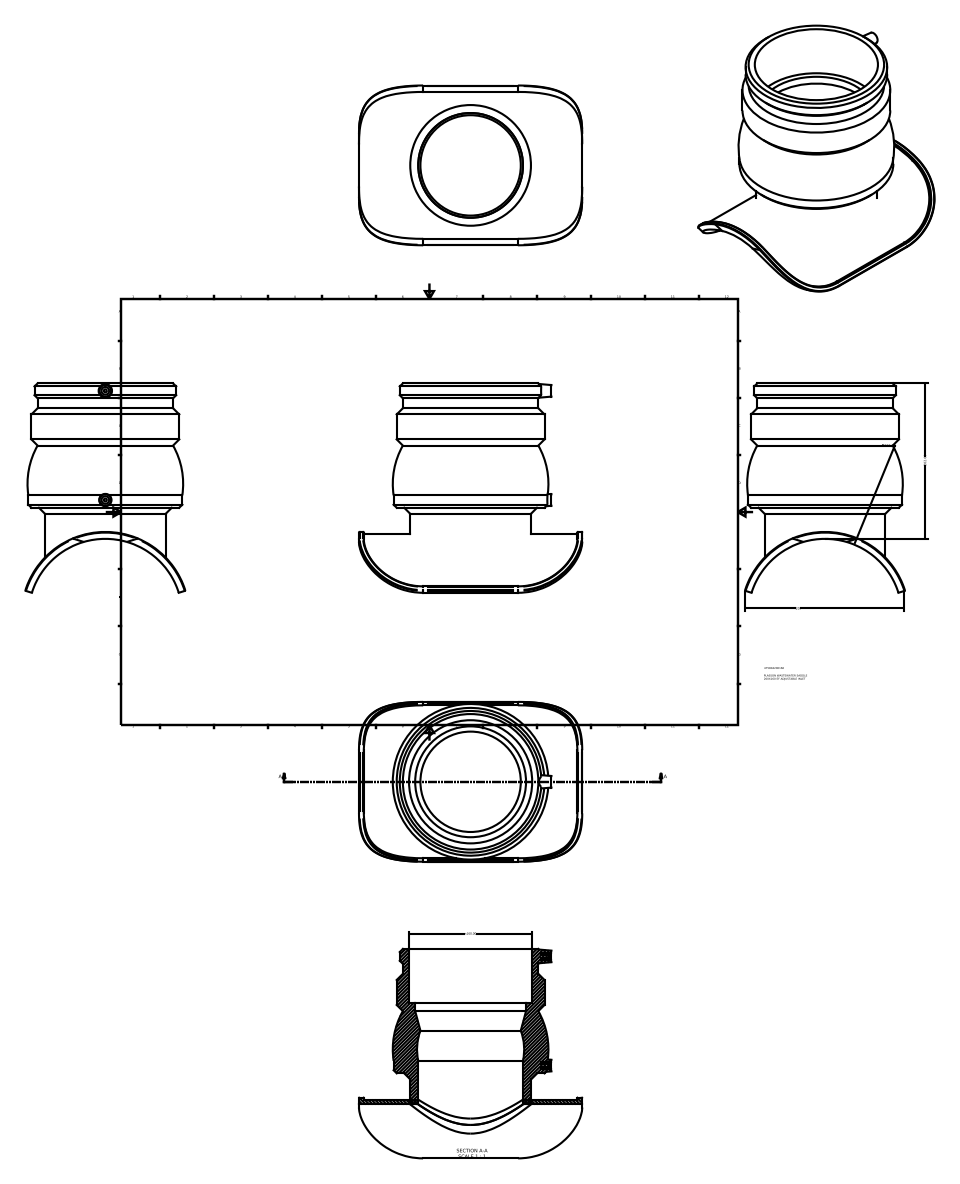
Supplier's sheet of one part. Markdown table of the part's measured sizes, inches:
| quantity | value |
| --- | --- |
| part name | 475804200160 |
| STEP written by | Autodesk Inventor 2015 (AUTOMOTIVE_DESIGN) |
| units | inches |
| bodies | 2 solids, 69 faces (17 planar, 29 cylindrical, 23 other) |
| overall size | 11.417 × 10.711 × 8.172 |
| volume | 152.5 in³ |
| surface area | 584.8 in² |
| round holes (diameter × count) | 0.394 × 2, 5.354 × 1, 5.669 × 1, 6.299 × 1 |
| round bosses / shafts (diameter × count) | 0.157 × 2, 7.874 × 1, 7.559 × 1, 7.244 × 1, 6.929 × 1, 6.173 × 1 |
| partial cylindrical surfaces (radius × count) | 0.033 × 4, 3.03 × 4, 3.276 × 4, 3.937 × 1, 4.183 × 1, 4.291 × 1 |
| main face-to-face distances | 6.362, 3.606, 2.756, 11.417, 0.246, 11.172, 0.245, 9.843, 1.575, 9.597 |
| hole center spacings | 5.583 |
